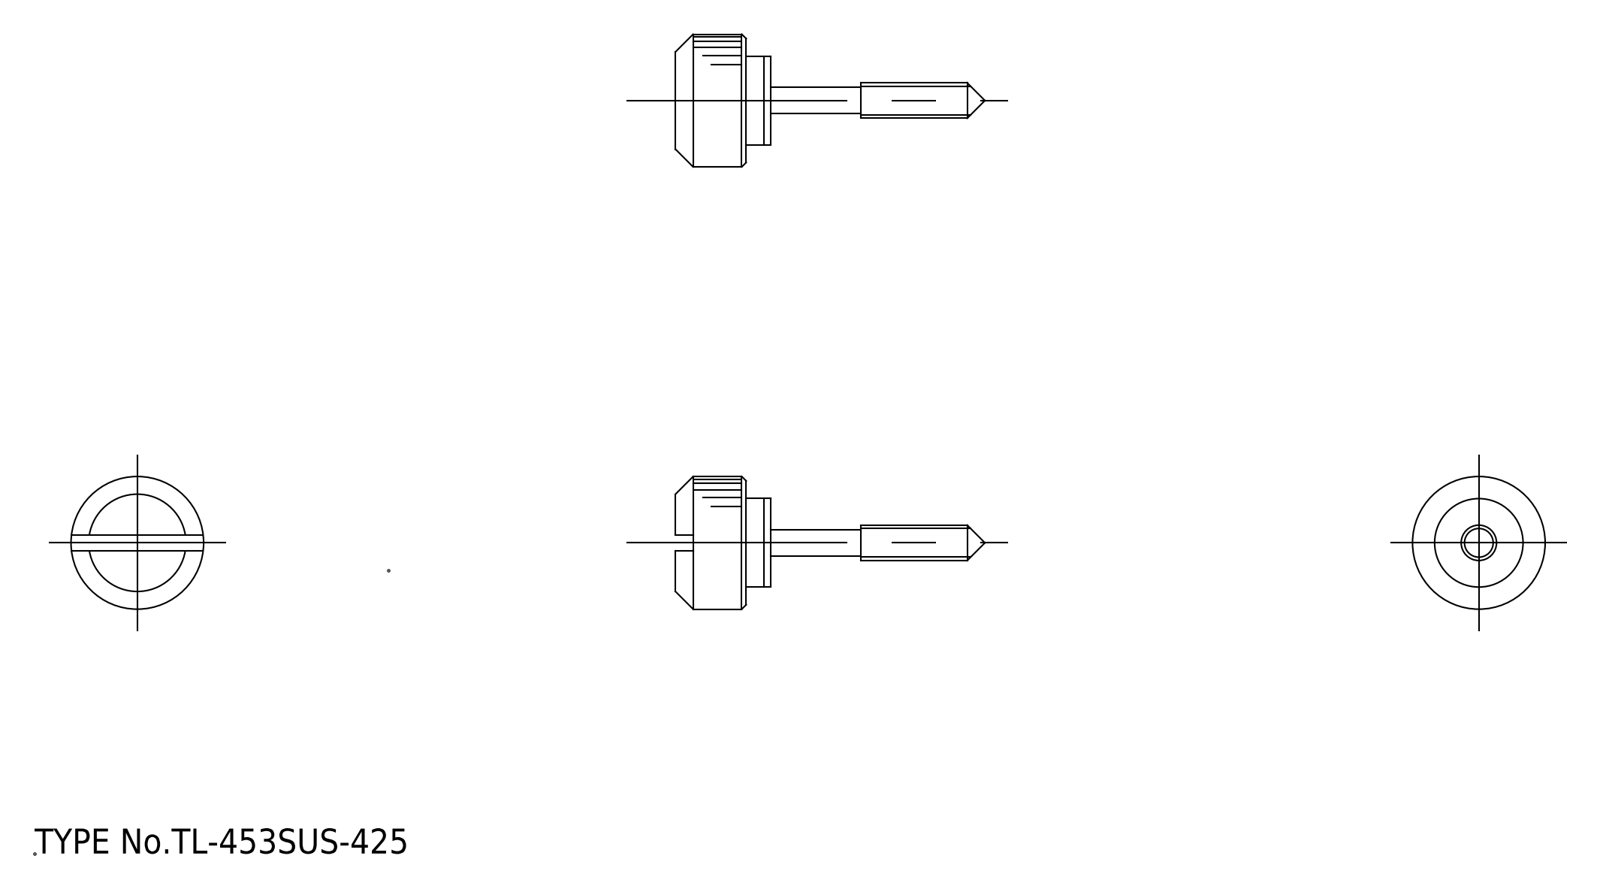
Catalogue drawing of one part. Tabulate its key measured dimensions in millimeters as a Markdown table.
| quantity | value |
| --- | --- |
| part name | washer; knob |
| STEP written by | spGate 19.8.4 (****-****-****-****) (AUTOMOTIVE_DESIGN) |
| units | millimeters |
| bodies | 2 solids, 38 faces (16 planar, 16 cylindrical, 6 other) |
| overall size | 35 × 15 × 15 |
| volume | 1 721 mm³ |
| surface area | 1 206 mm² |
| round bosses / shafts (diameter × count) | 15 × 1, 10 × 1, 4 × 1, 3 × 1 |
| partial cylindrical surfaces (radius × count) | 0.8 × 3, 1.55 × 1 |
| main face-to-face distances | 2, 8, 10, 10.8, 2.8, 0.8, 6, 8.8, 1.8, 21 |
